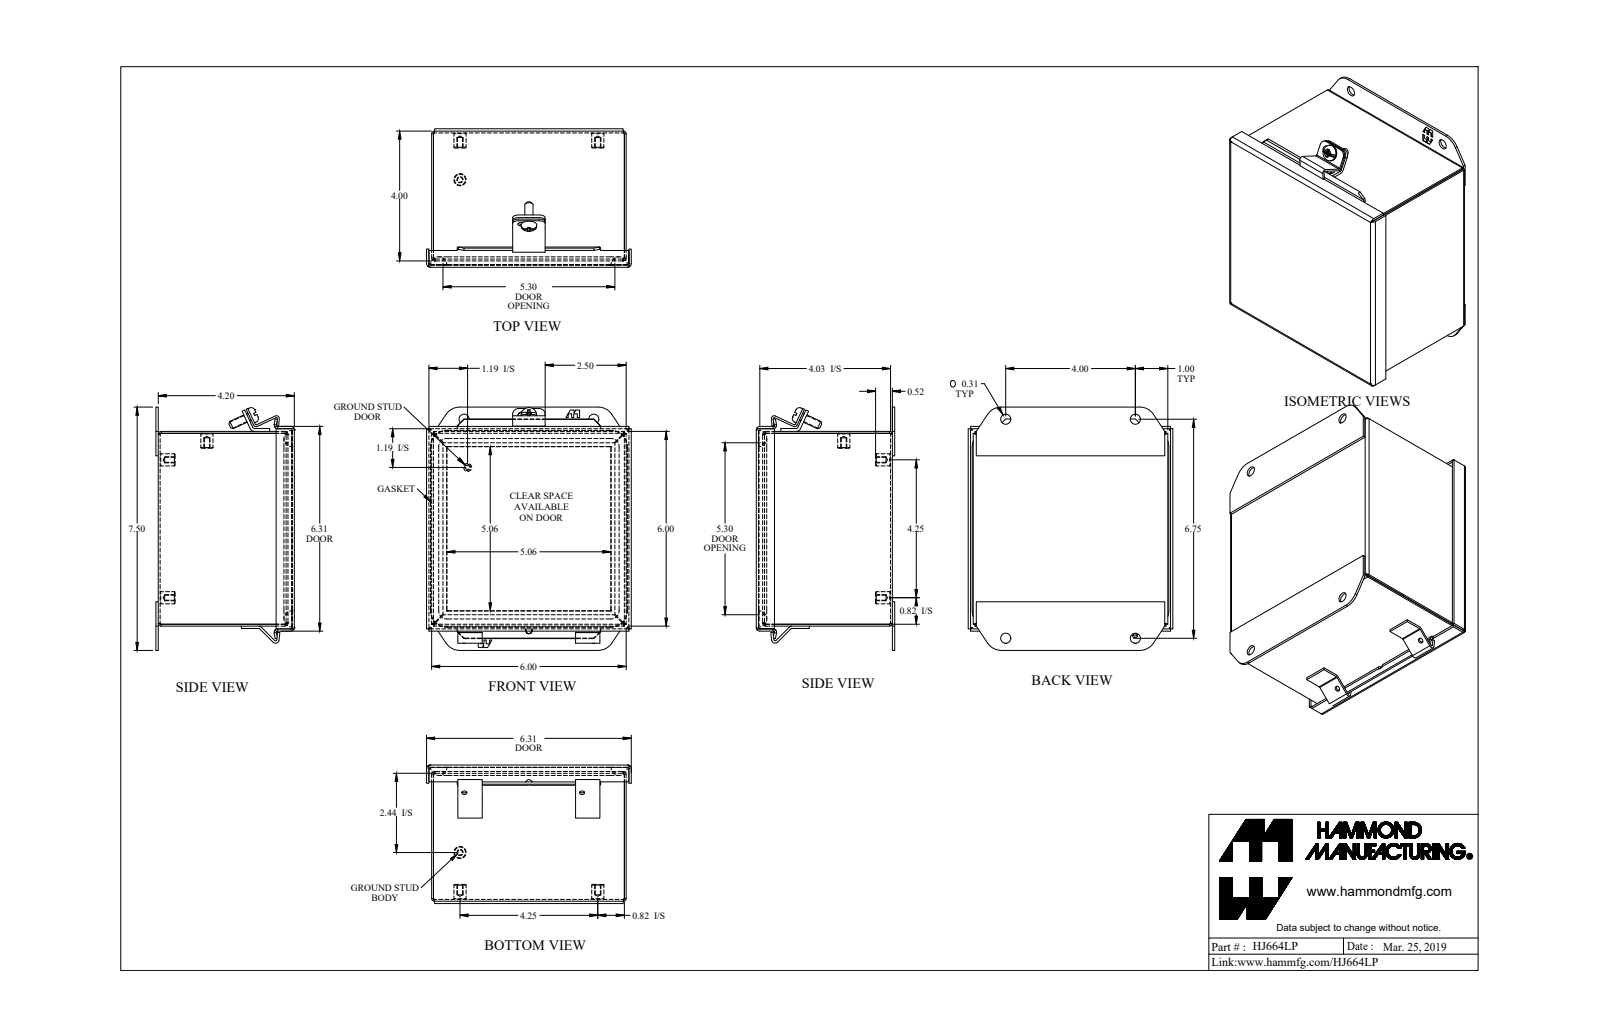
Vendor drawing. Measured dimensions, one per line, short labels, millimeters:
name: HJ664LP
written by: SolidWorks 2018 (AUTOMOTIVE_DESIGN)
unit: mm
bodies: 16 solids, 518 faces (282 planar, 136 cylindrical, 100 other)
size: 190.5 × 160.3 × 108.4
volume: 252 500 mm³; area: 311 100 mm²
holes: 5× ⌀4, 4× ⌀8, 2× ⌀4, 1× ⌀5.4
bosses: 5× ⌀9.5, 2× ⌀6.4, 1× ⌀12.2, 1× ⌀4.8
rounds: 14× R4.8, 10× R0.7, 10× R2.2, 8× R0.9, 8× R2.7, 4× R6.4, 4× R12.7, 4× R12.7
face distances: 1.4, 151, 1.8, 106.6, 104.8, 152.4, 149.5, 1.4, 103.3, 105.2
hole spacings: 108, 109.5, 31.9, 31.9, 101.6, 139.7, 139.8, 152.7
